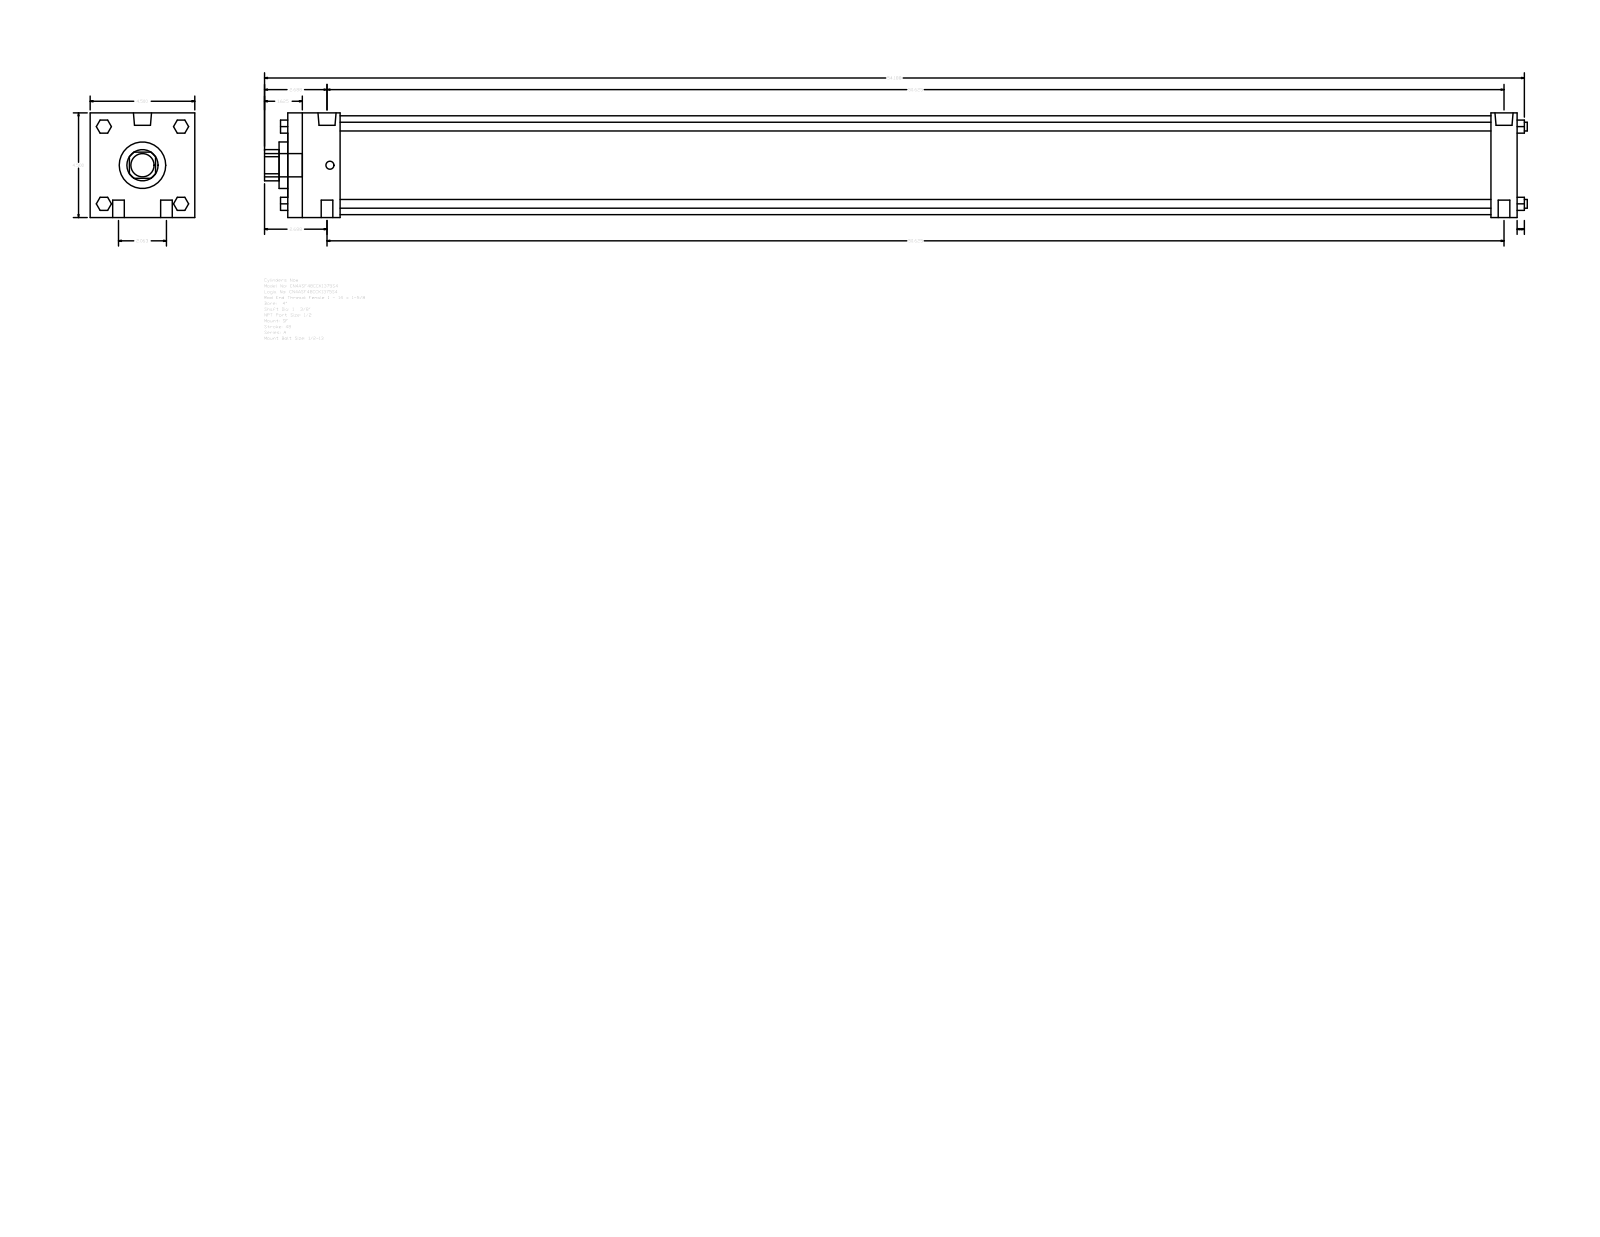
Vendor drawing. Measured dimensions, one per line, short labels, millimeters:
name: A_SF__0400_1.375
written by: GSSL Pune (CONFIG_CONTROL_DESIGN)
unit: mm
bodies: 0 solids, 124 faces (94 planar, 30 cylindrical, 0 other)
size: 1379.54 × 114.3 × 114.3
holes: 1× ⌀34.92, 1× ⌀50.8, 1× ⌀107.95
bosses: 4× ⌀12.7, 4× ⌀9.53, 2× ⌀19.77, 2× ⌀8.73, 1× ⌀25.4
rounds: 1× R17.06
face distances: 114.3, 1343.02, 28.57, 1314.45, 57.15, 1257.3, 1285.87, 14.29, 9.52, 66.67
